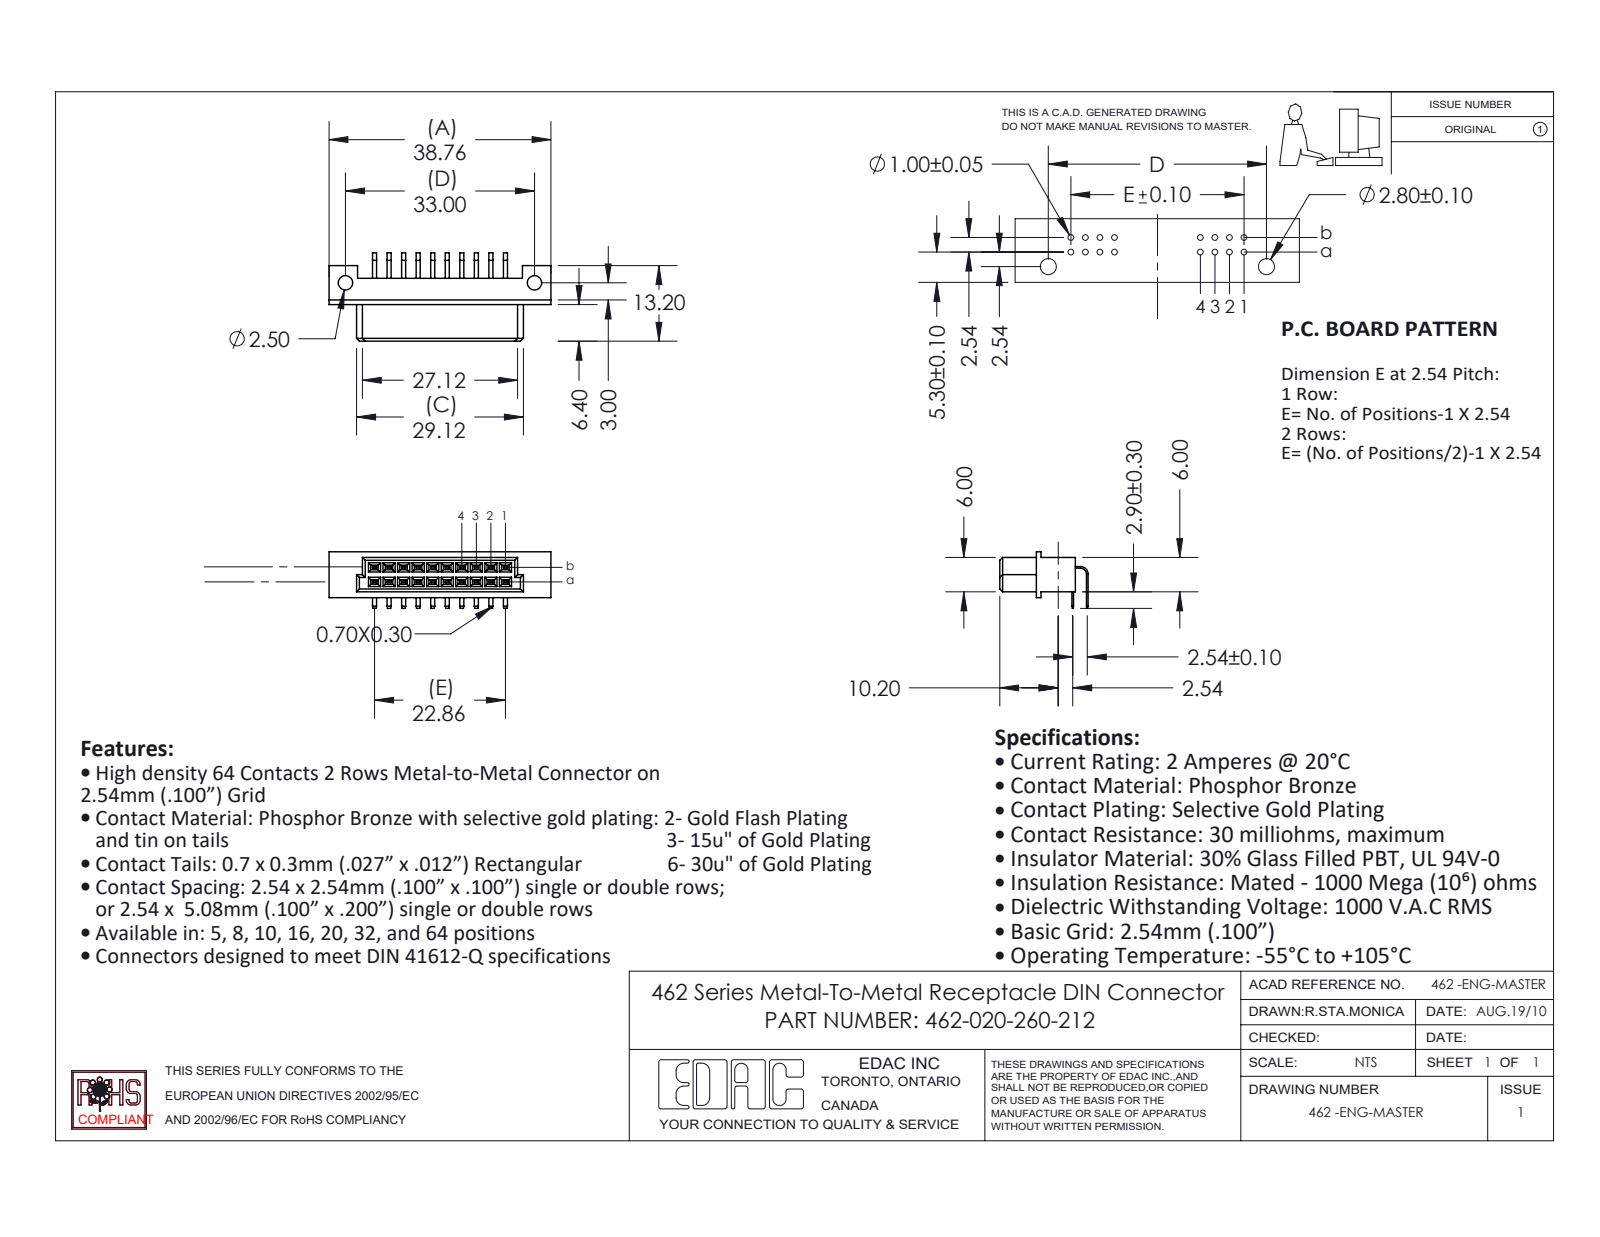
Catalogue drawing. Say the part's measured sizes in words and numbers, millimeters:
The part is named "462-290-2; 462-020-260-212; 462-290-1; 462 Part_20". Its 3-D file was written by "SolidWorks 2020 (CONFIG_CONTROL_DESIGN)". It is 21 solids with 575 faces: 531 planar, 44 cylindrical and 0 other. Overall it measures 38.76 by 15.43 by 9.9 millimeters. Its volume is 2 160 cubic millimeters and its surface area 2 803 square millimeters. Round holes: 2 of diameter 2.5. Partial cylindrical surfaces (rounded edges, fillets, slot ends): 2 of radius 1.02, 2 of radius 1.32. The main face-to-face distances are 2.54, 6, 4.6, 0.81, 1.58, 1.88, 4.12, 4.42, 0.56, 0.55. The hole center spacings are 33.
